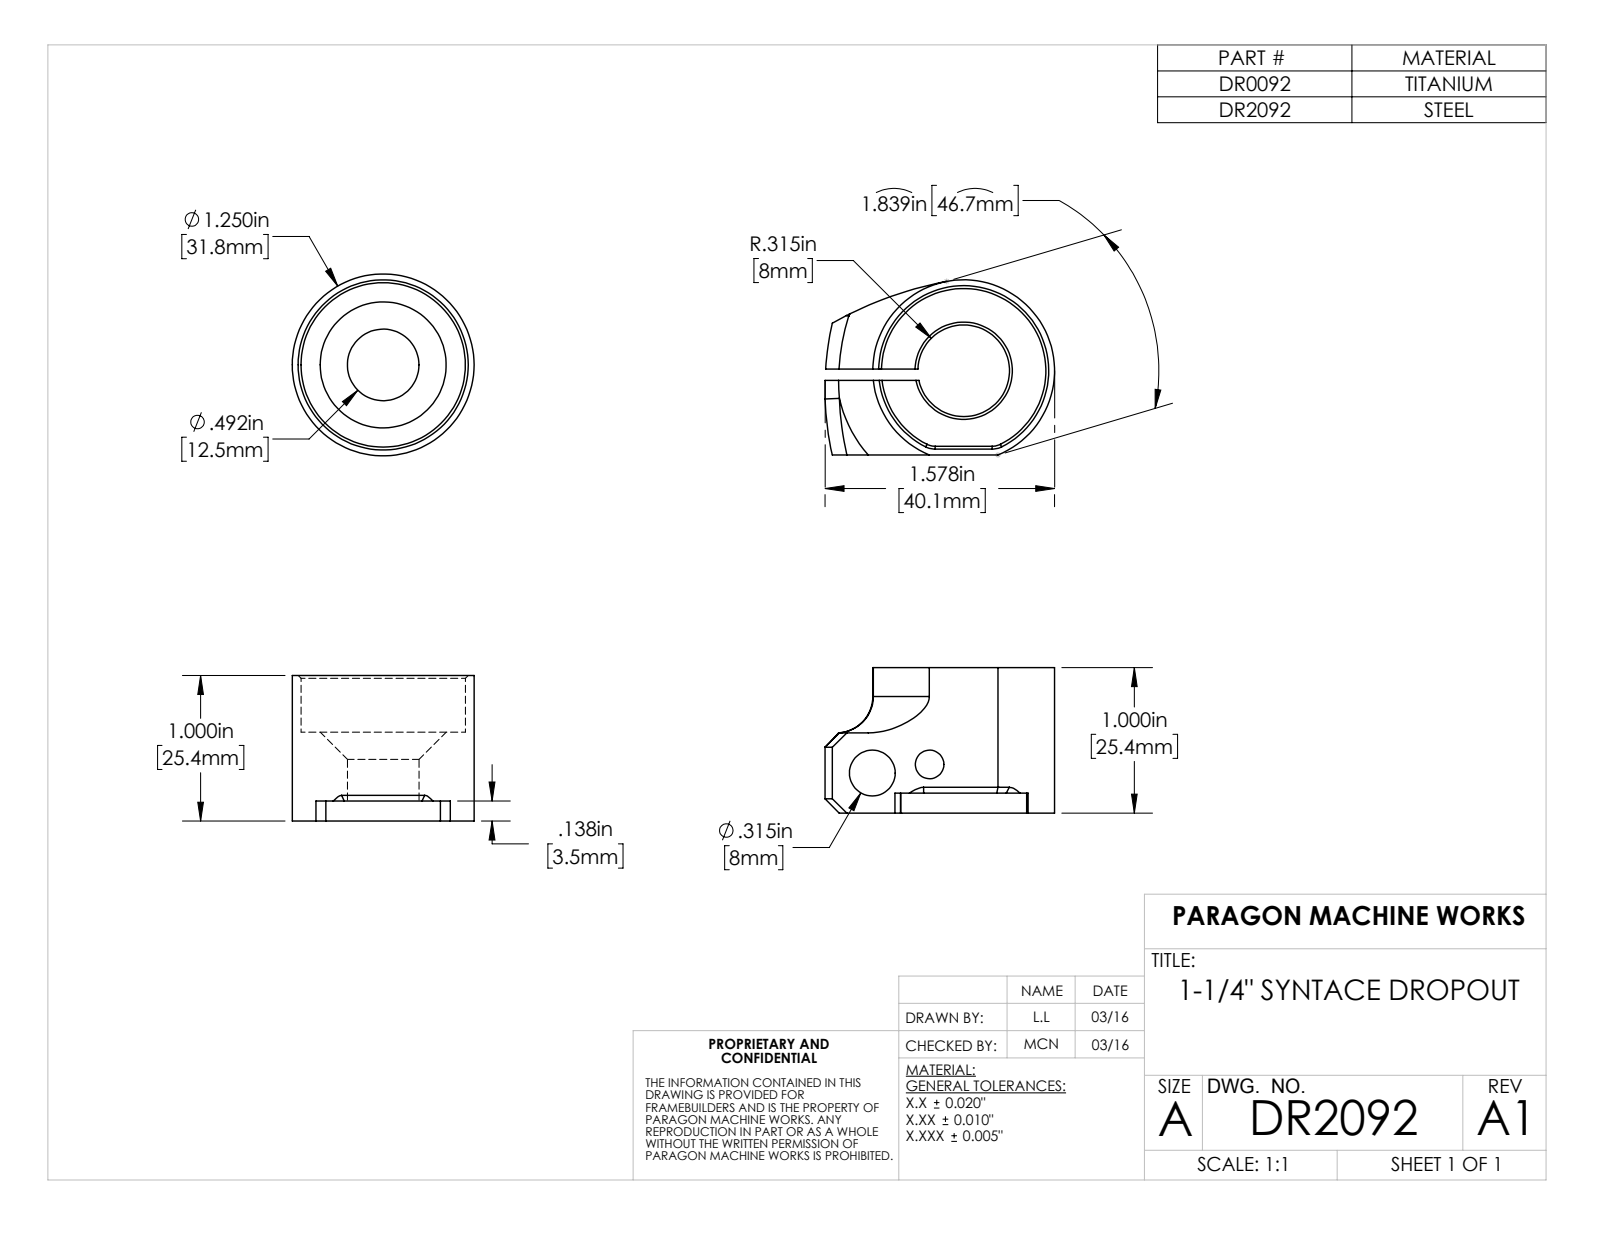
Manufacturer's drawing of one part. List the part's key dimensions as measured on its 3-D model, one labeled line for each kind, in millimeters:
Part name (STEP PRODUCT): DR2092; DR4090; DR2092R; DR2092L
STEP written by: SolidWorks 2016 (AUTOMOTIVE_DESIGN)
Units: millimetres
Bodies: 3 solids, 118 faces (33 planar, 47 cylindrical, 38 other)
Overall size (bounding box): 185.8 × 58.87 × 54.41
Volume: 23 967 mm³ · Surface area: 14 562 mm²
Round holes (diameter × count): ⌀5 ×1, ⌀7 ×1, ⌀8 ×1, ⌀9 ×1, ⌀11 ×1, ⌀12.5 ×1, ⌀16 ×1, ⌀28.7 ×1
Round bosses / shafts (diameter × count): ⌀31.75 ×1, ⌀15 ×1
Partial cylindrical surfaces — rounded edges, fillets, slot ends (radius × count): R1 ×3, R3.2 ×2, R0.25 ×1, R1.5 ×1, R2.5 ×1, R5 ×1, R10 ×1, R11 ×1
Main face-to-face distances: 3.5, 138.5, 4.5, 12.5, 151, 8, 1.5, 14, 9, 10.5
Hole centre spacings: 10.11, 44.27
